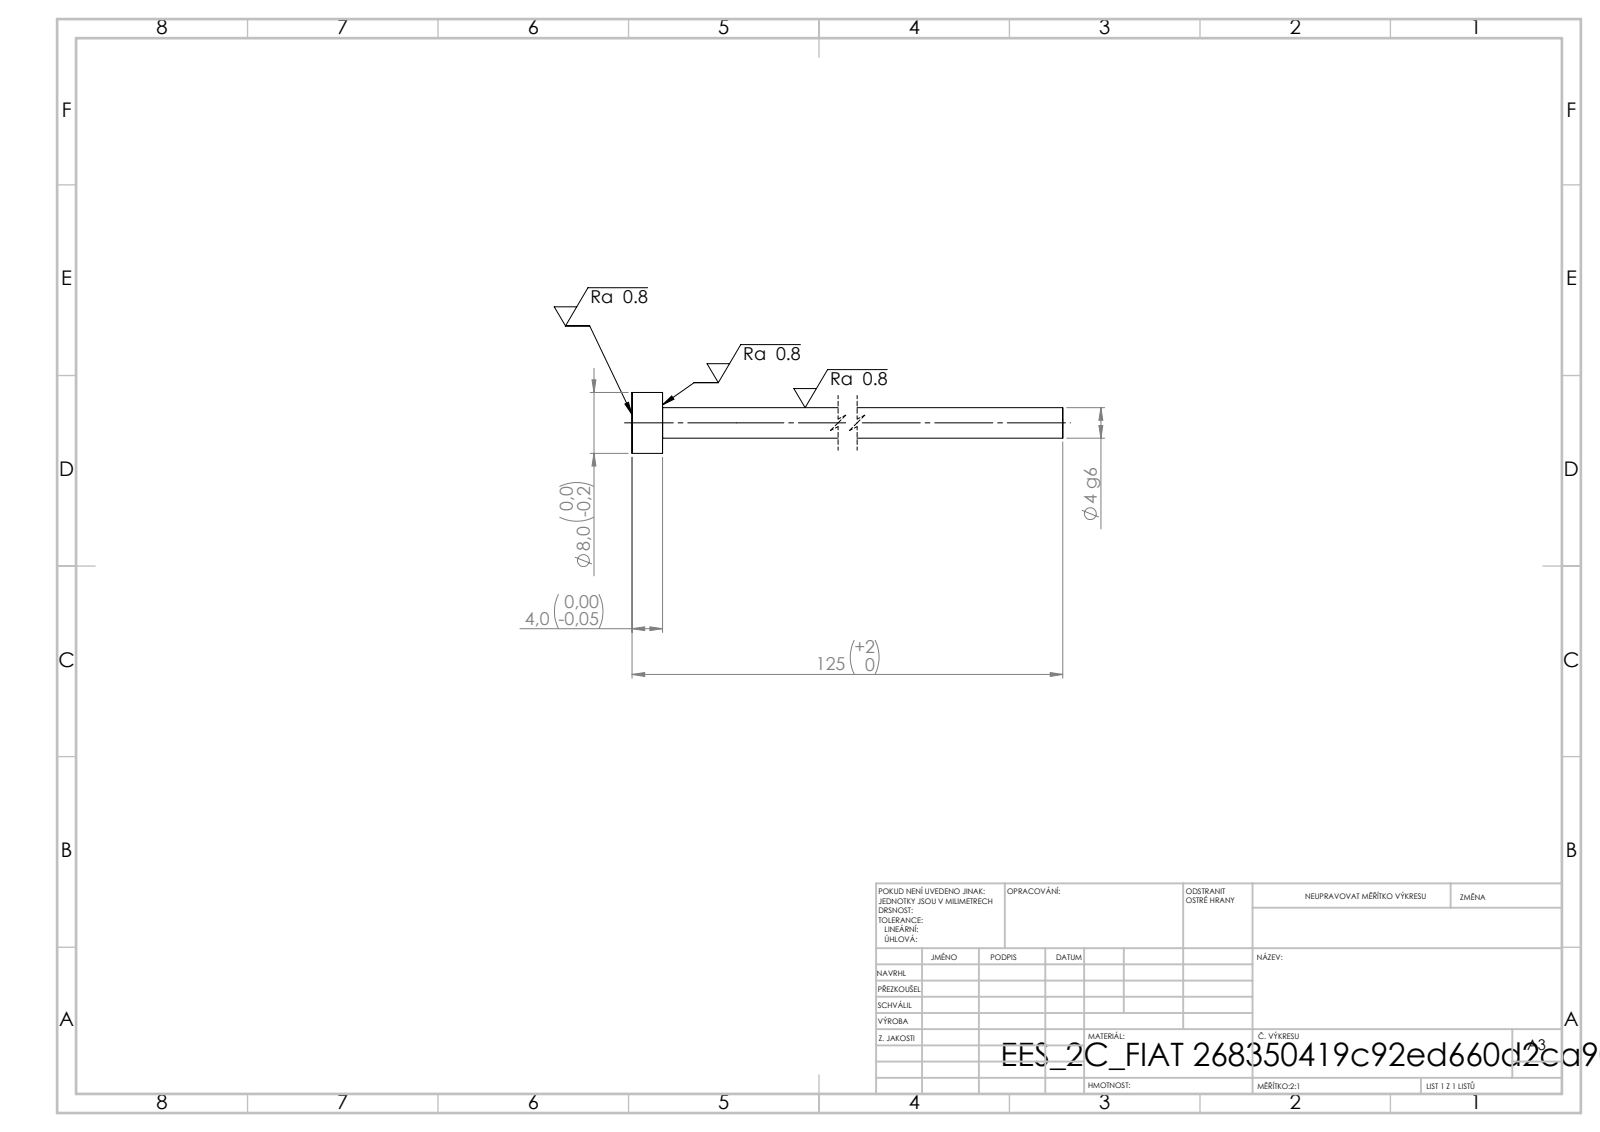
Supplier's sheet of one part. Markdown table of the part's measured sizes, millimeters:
| quantity | value |
| --- | --- |
| STEP written by | SolidWorks 2019 (CONFIG_CONTROL_DESIGN) |
| units | millimeters |
| bodies | 1 solid, 7 faces (3 planar, 4 cylindrical, 0 other) |
| overall size | 125 × 8 × 8 |
| volume | 1 722 mm³ |
| surface area | 1 722 mm² |
| round bosses / shafts (diameter × count) | 8 × 1, 4 × 1 |
| main face-to-face distances | 4, 125, 121 |
